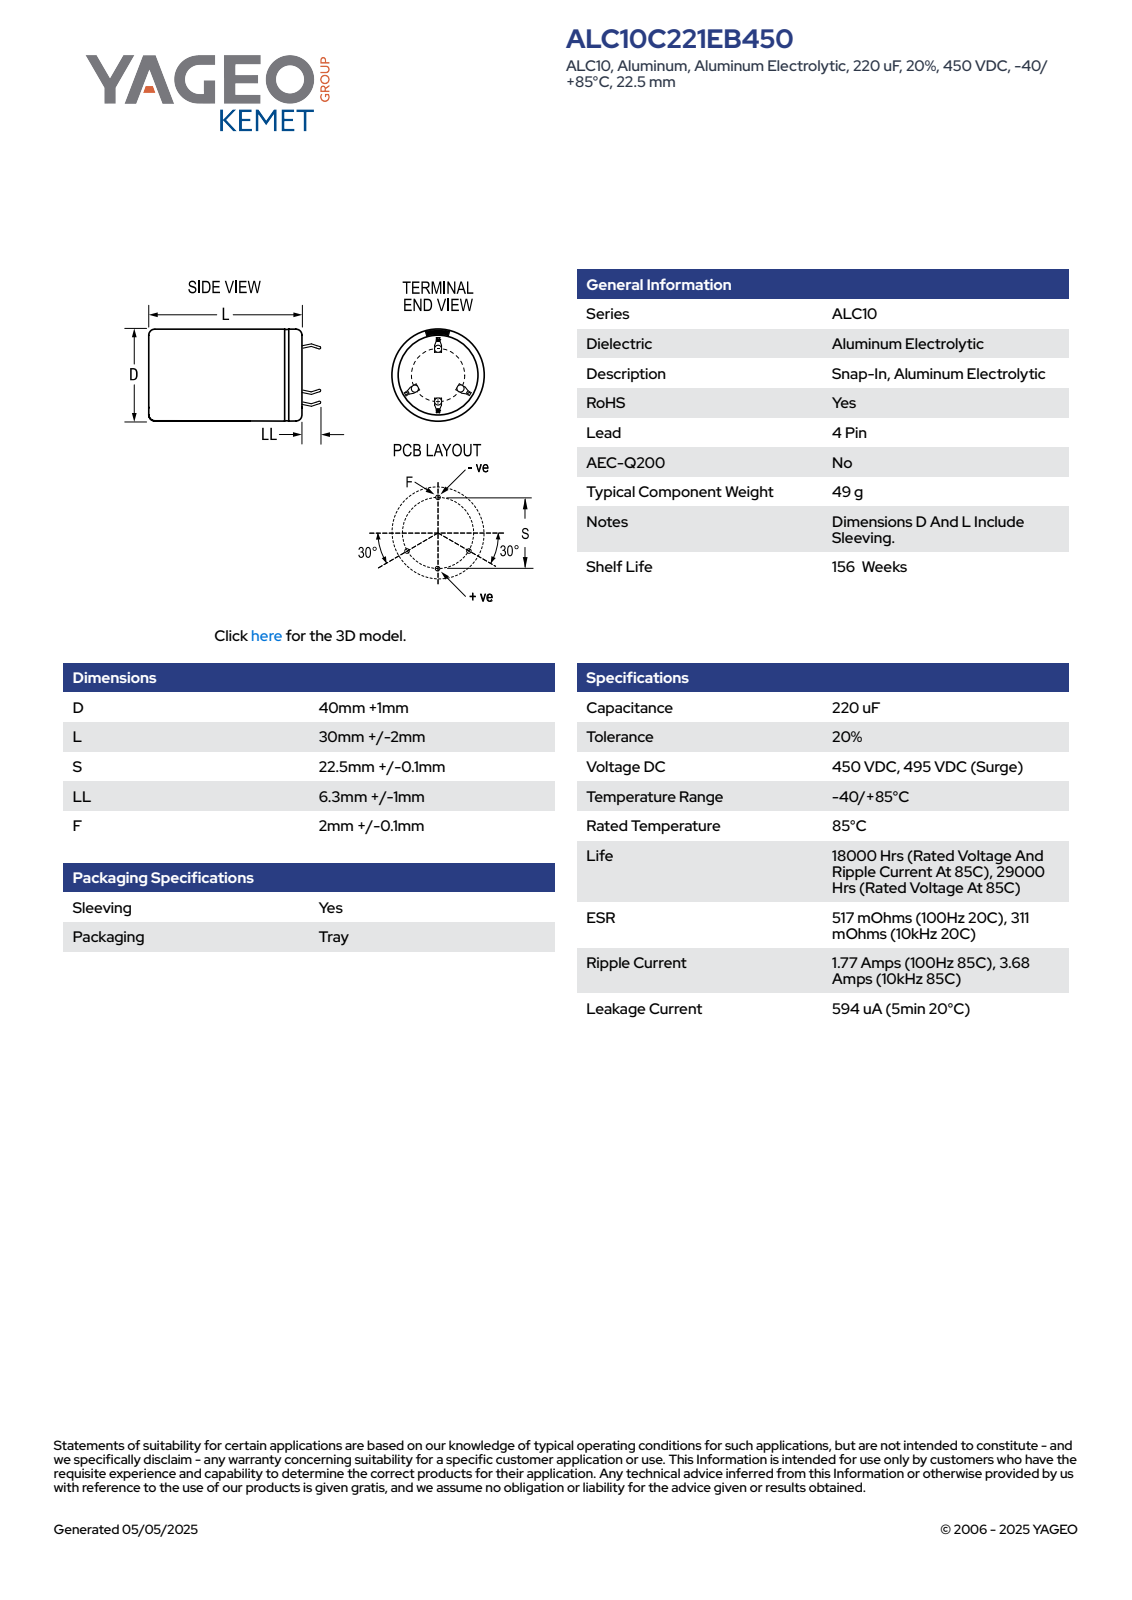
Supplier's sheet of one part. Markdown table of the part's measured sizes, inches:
| quantity | value |
| --- | --- |
| part name | CARS_K4P_40X30_D41L32S22.5LL7.3F2.1 |
| STEP written by | SolidWorks 2014 (AUTOMOTIVE_DESIGN) |
| units | inches |
| bodies | 1 solid, 134 faces (80 planar, 15 cylindrical, 39 other) |
| overall size | 1.614 × 1.614 × 1.547 |
| volume | 2.531 in³ |
| surface area | 10.55 in² |
| round holes (diameter × count) | 1.428 × 1 |
| round bosses / shafts (diameter × count) | 1.614 × 1 |
| partial cylindrical surfaces (radius × count) | 0.807 × 1 |
| main face-to-face distances | 1.259, 1.279, 0.02, 0.024, 0.017, 0.817, 0.03, 0.053, 0.8, 0.833 |
